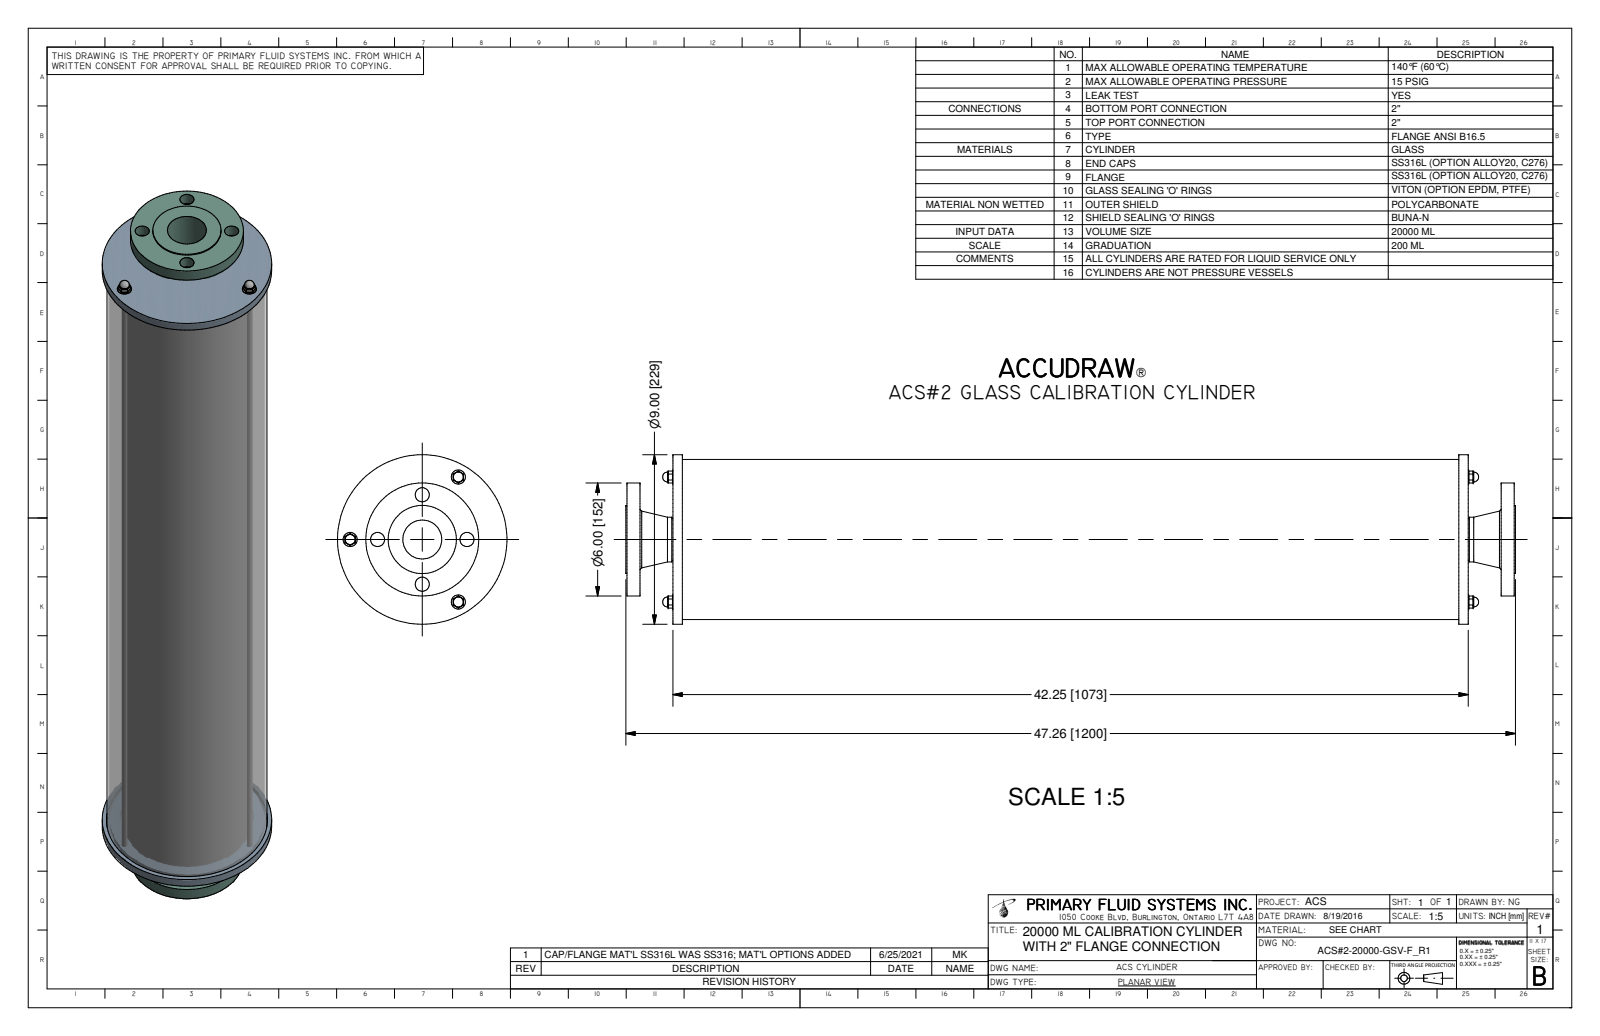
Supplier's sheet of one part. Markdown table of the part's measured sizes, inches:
| quantity | value |
| --- | --- |
| part name | ACS#2-20000-GSV-F_R0; ACS-3-20000-METAL-S_R1; ACS-2-20000_R6; ACS-1-20000-A_R0 (+4 more) |
| STEP written by | Autodesk Inventor 2009 (AUTOMOTIVE_DESIGN) |
| units | inches |
| bodies | 21 solids, 245 faces (88 planar, 129 cylindrical, 28 other) |
| overall size | 47.255 × 9 × 9 |
| volume | 472.6 in³ |
| surface area | 4 589 in² |
| round holes (diameter × count) | 0.75 × 4, 0.328 × 3, 0.344 × 3, 2.067 × 1, 6.252 × 1, 7.125 × 1, 8.25 × 1, 8.55 × 1 |
| round bosses / shafts (diameter × count) | 0.75 × 3, 0.528 × 3, 0.313 × 3, 9 × 1, 8.5 × 1, 8.2 × 1, 6.804 × 1, 6.165 × 1 |
| partial cylindrical surfaces (radius × count) | 0.005 × 60 |
| main face-to-face distances | 42.25, 0.5, 41.75, 1.75, 2.25, 43.5, 44, 0.69, 2.44, 2.94 |
| hole center spacings | 2.375, 3.359, 3.831, 6.636, 2.135, 3.35, 4.508, 4.75 |
